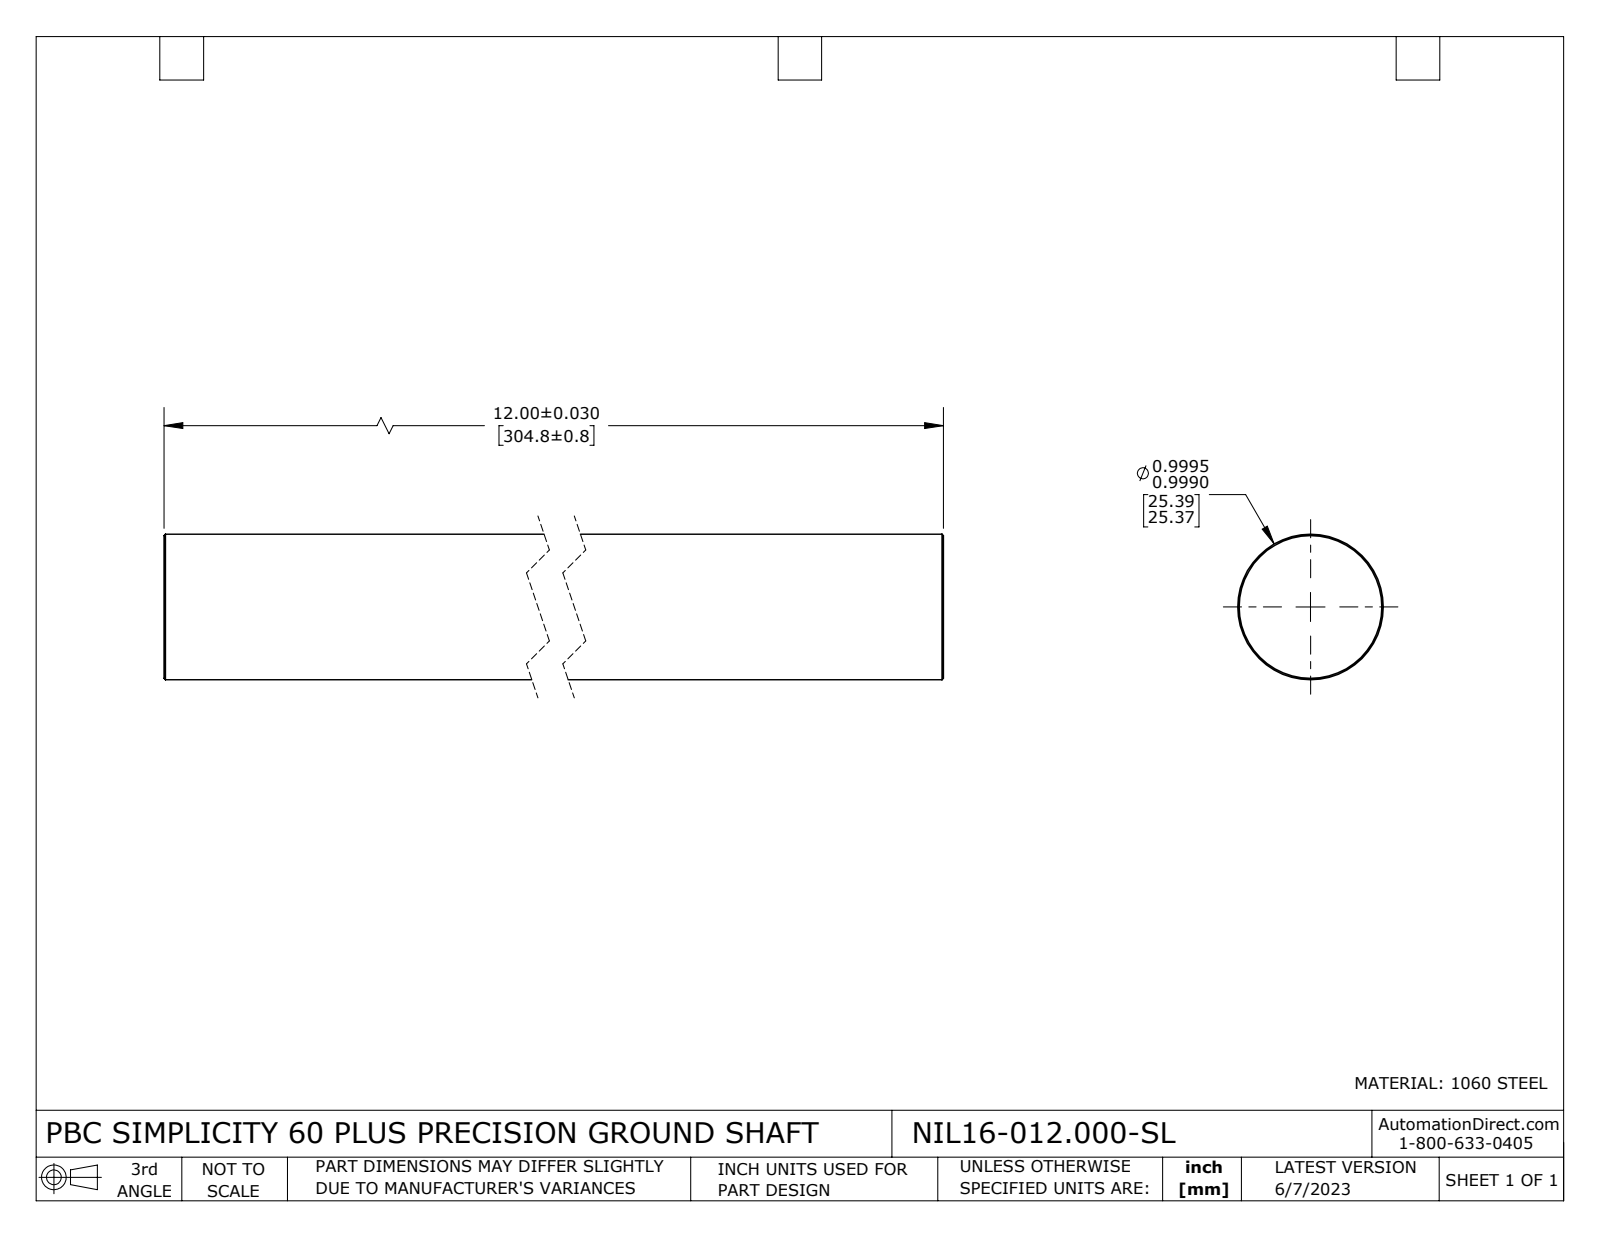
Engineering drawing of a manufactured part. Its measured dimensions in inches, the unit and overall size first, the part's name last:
Units: inches
Overall size (bounding box): 12 × 1 × 1
Round bosses / shafts (diameter × count): ⌀1 ×1
Main face-to-face distances: 12
Volume: 9.424 in³ · Surface area: 39.23 in²
Bodies: 1 solid, 8 faces (2 planar, 2 cylindrical, 4 other)
Part name (STEP PRODUCT): NIL16-012.000-SL
STEP written by: SolidWorks 2021 (CONFIG_CONTROL_DESIGN)
